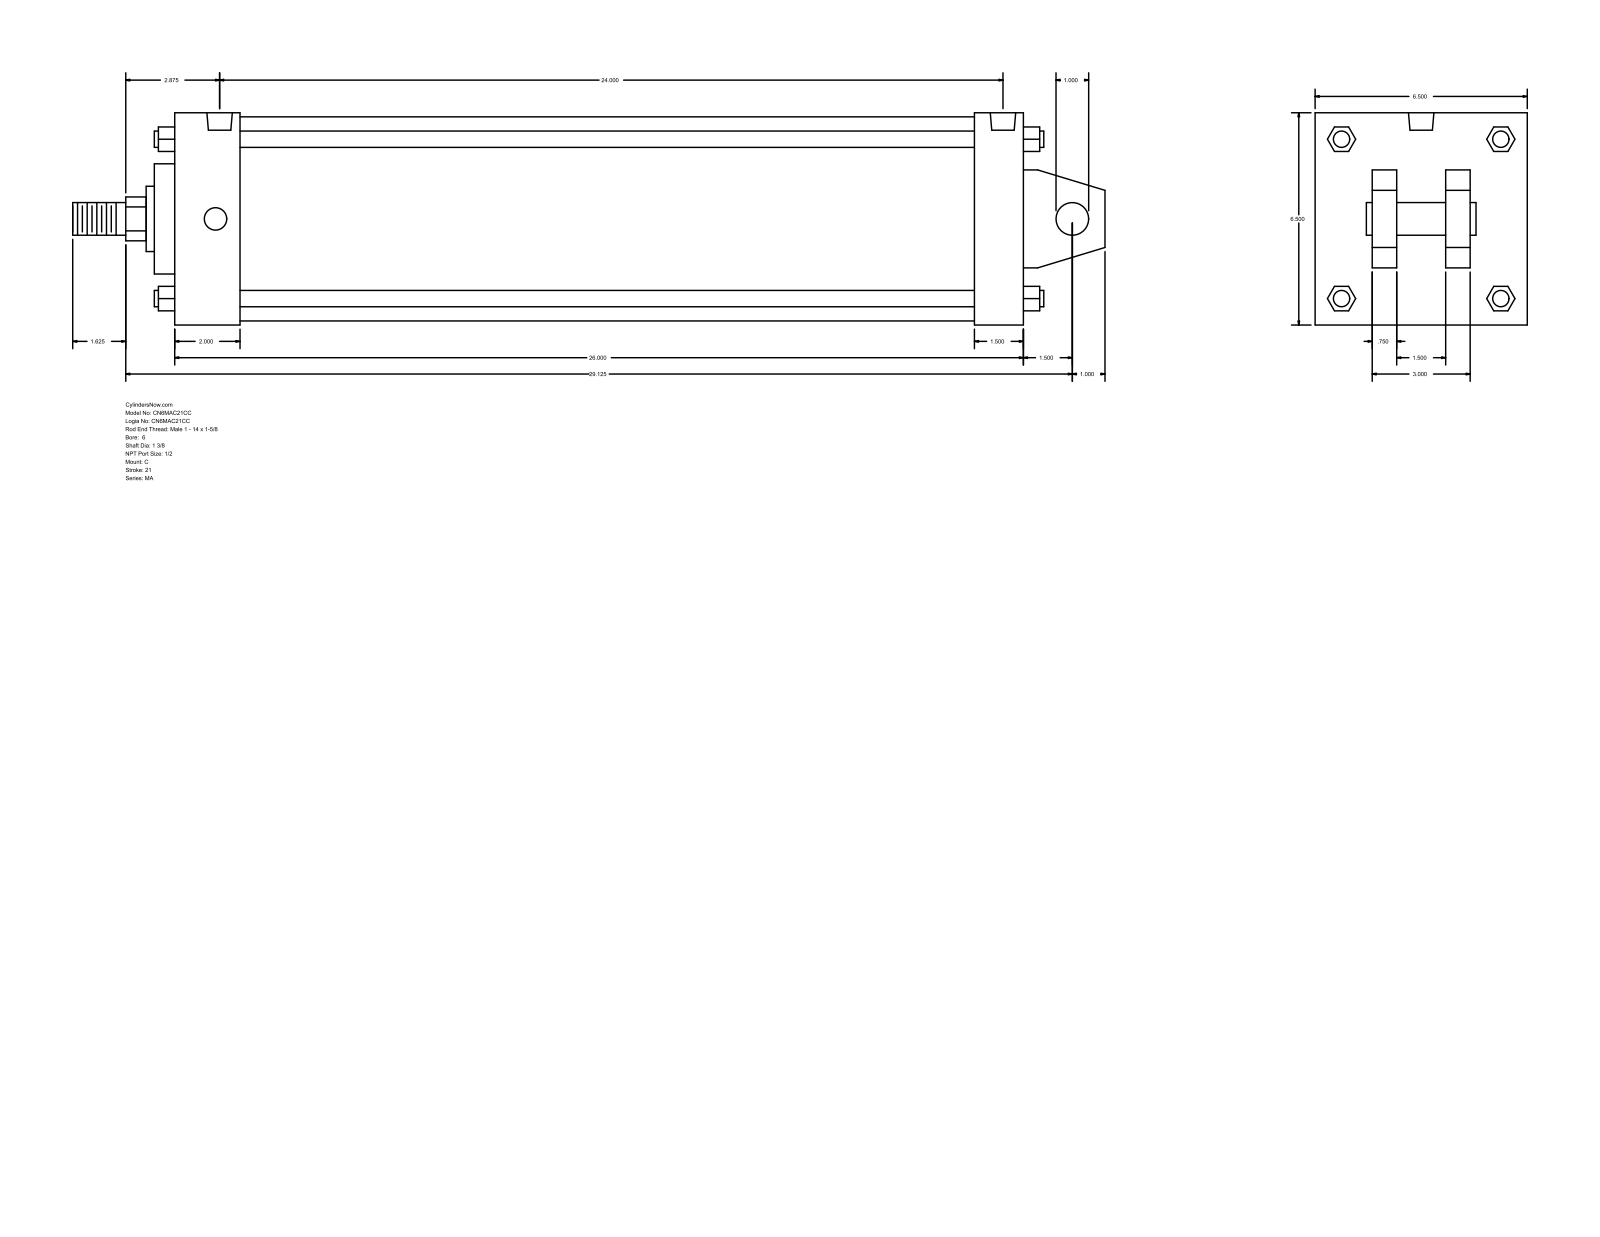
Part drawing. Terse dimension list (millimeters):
name: MA_C__0600_1.375
written by: GSSL Pune (CONFIG_CONTROL_DESIGN)
unit: mm
bodies: 0 solids, 141 faces (109 planar, 32 cylindrical, 0 other)
size: 803.27 × 165.1 × 165.1
holes: 4× ⌀17.46, 2× ⌀19.77
bosses: 4× ⌀12.7, 2× ⌀25.4, 1× ⌀158.75, 1× ⌀85.72, 1× ⌀50.8, 1× ⌀34.92
rounds: 1× R17.06
face distances: 165.1, 660.4, 38.1, 19.05, 63.5, 101.6, 50.8, 44.45, 120.65, 622.3
hole spacings: 609.6, 3.17, 3.18, 606.42, 609.59, 612.77
